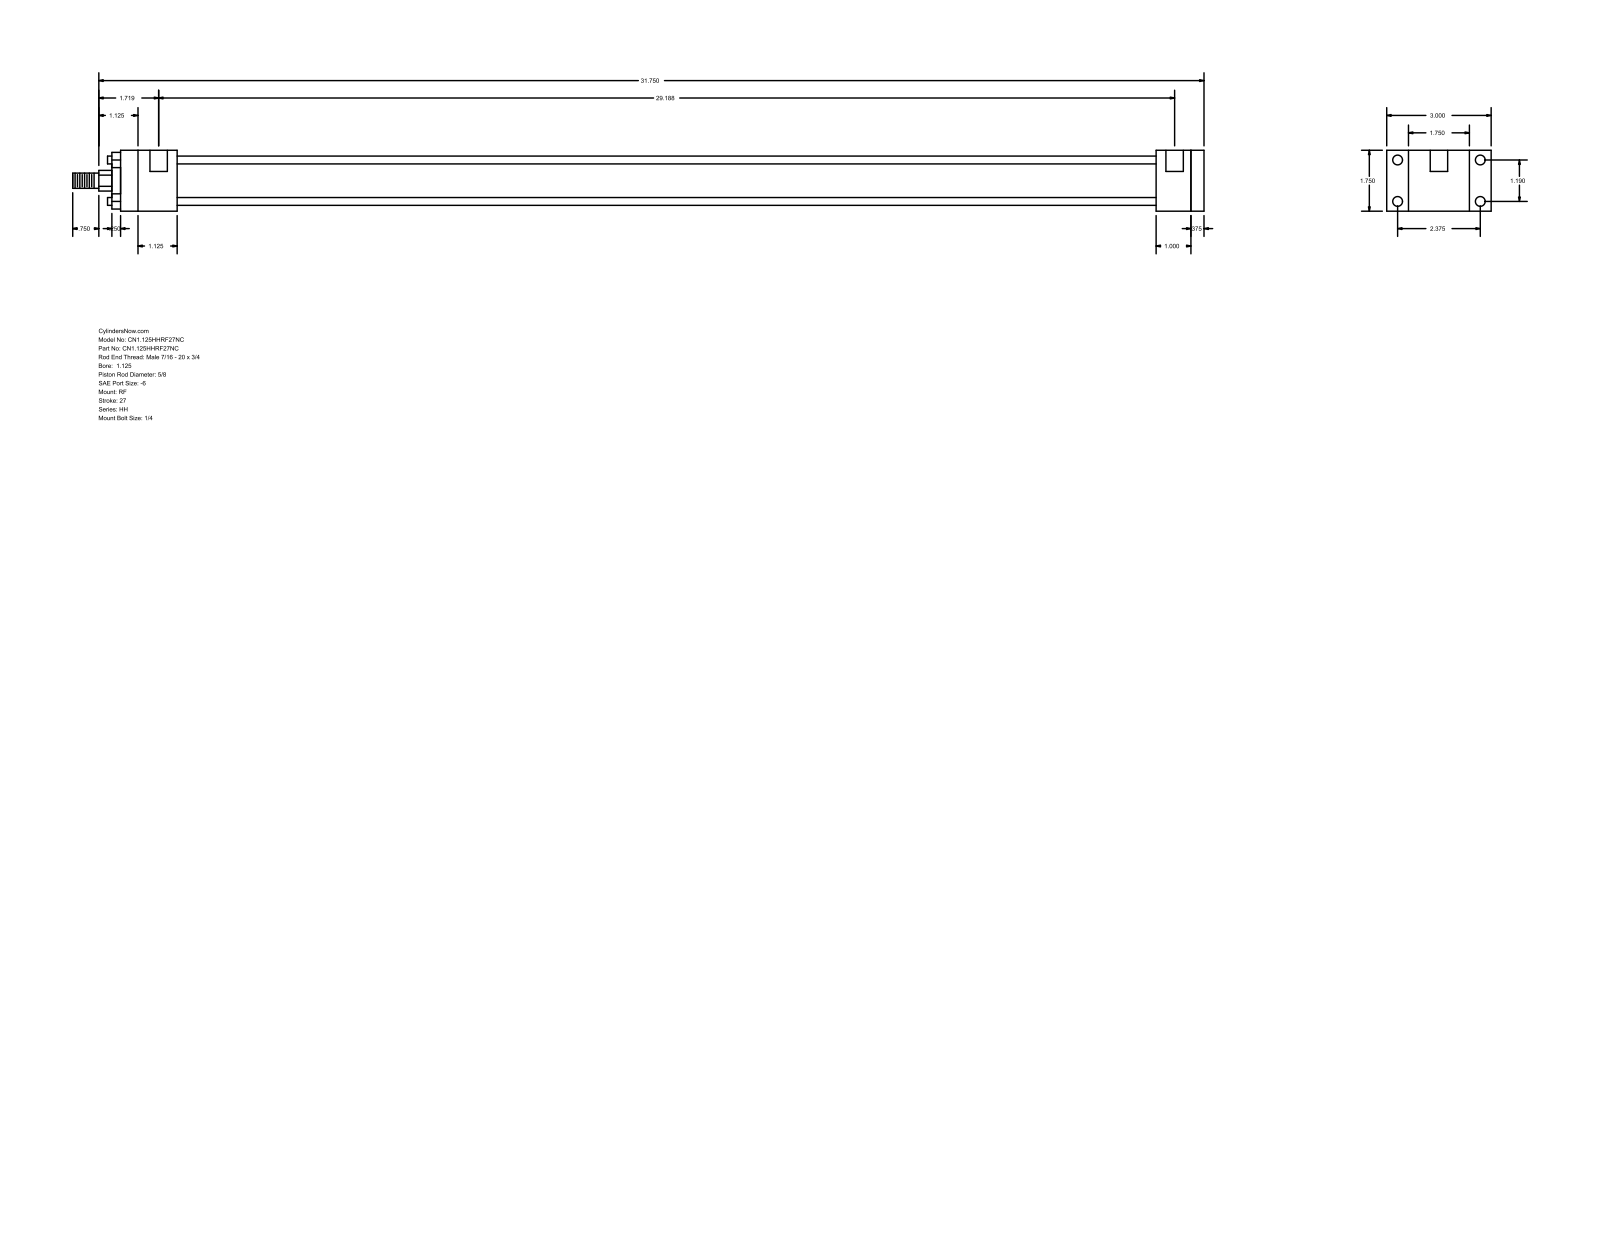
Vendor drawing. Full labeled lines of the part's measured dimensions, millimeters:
Part name (STEP PRODUCT): HH_RF__0112_0.625
STEP written by: GSSL Pune (CONFIG_CONTROL_DESIGN)
Units: millimetres
Bodies: 0 solids, 92 faces (64 planar, 28 cylindrical, 0 other)
Overall size (bounding box): 825.5 × 76.2 × 44.45
Round holes (diameter × count): ⌀5.56 ×4, ⌀7.14 ×4, ⌀12.7 ×2
Round bosses / shafts (diameter × count): ⌀5.71 ×4, ⌀34.92 ×1, ⌀28.57 ×1, ⌀15.88 ×1, ⌀11.11 ×1
Partial cylindrical surfaces — rounded edges, fillets, slot ends (radius × count): R7.54 ×1
Main face-to-face distances: 44.46, 9.53, 790.57, 25.4, 34.93, 15.87, 739.77, 749.3, 714.37, 41.27
Hole centre spacings: 30.22, 60.32, 67.47, 738.19, 3.17, 741.36
